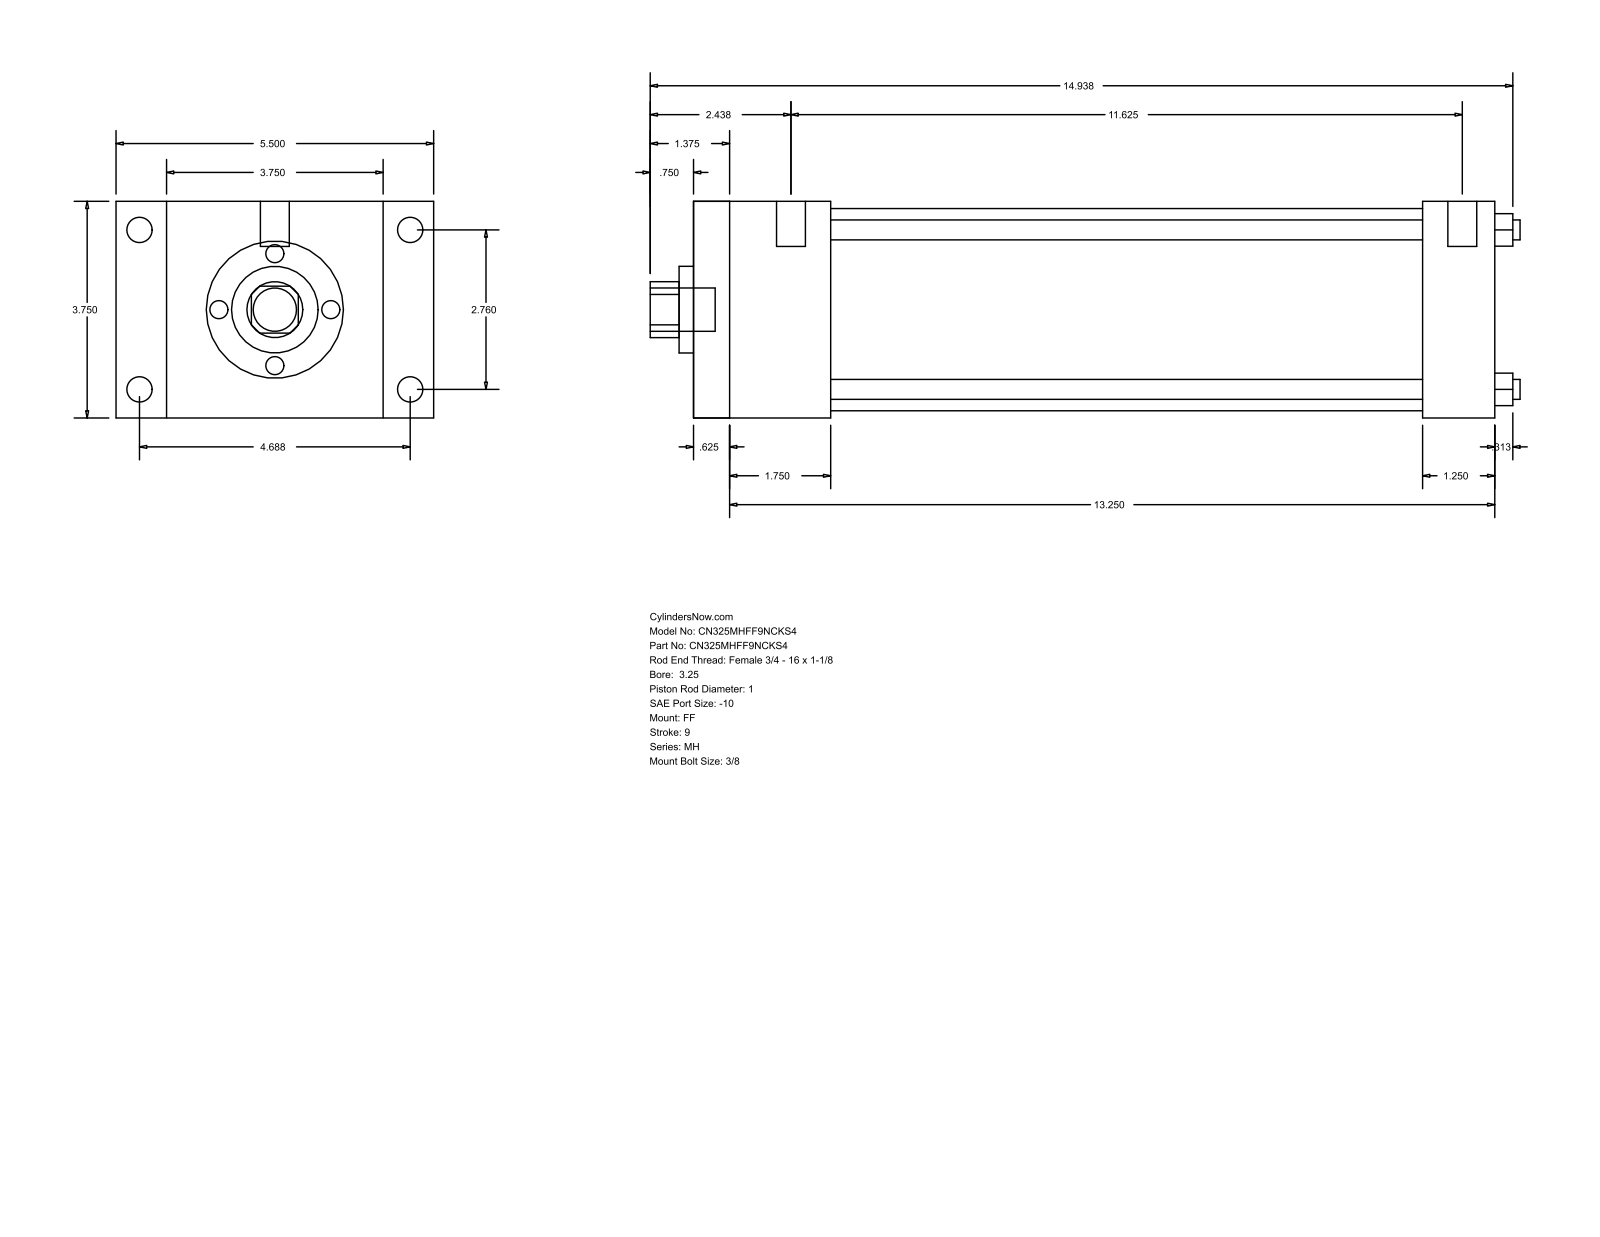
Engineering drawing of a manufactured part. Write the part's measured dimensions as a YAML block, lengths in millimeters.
part_name: "MH_FF__0325_1"
step_written_by: "GSSL Pune (CONFIG_CONTROL_DESIGN)"
units: millimeters
bodies: {solids: 0, faces: 92, planar: 64, cylindrical: 28, other: 0}
overall_size: [382.59, 139.7, 95.25]
round_holes:
  - {diameter: 8.76, count: 4}
  - {diameter: 25.4, count: 1}
  - {diameter: 38.1, count: 1}
  - {diameter: 88.9, count: 1}
round_bosses_or_shafts:
  - {diameter: 11.13, count: 4}
  - {diameter: 5.56, count: 4}
  - {diameter: 12.7, count: 2}
  - {diameter: 19.05, count: 1}
partial_cylinders:
  - {radius: 12.29, count: 1}
face_to_face_distances: [95.24, 352.43, 15.87, 336.56, 22.23, 117.47, 320.68, 304.81, 31.75, 60.33]
hole_center_spacings: [49.57, 70.1, 99.14]
